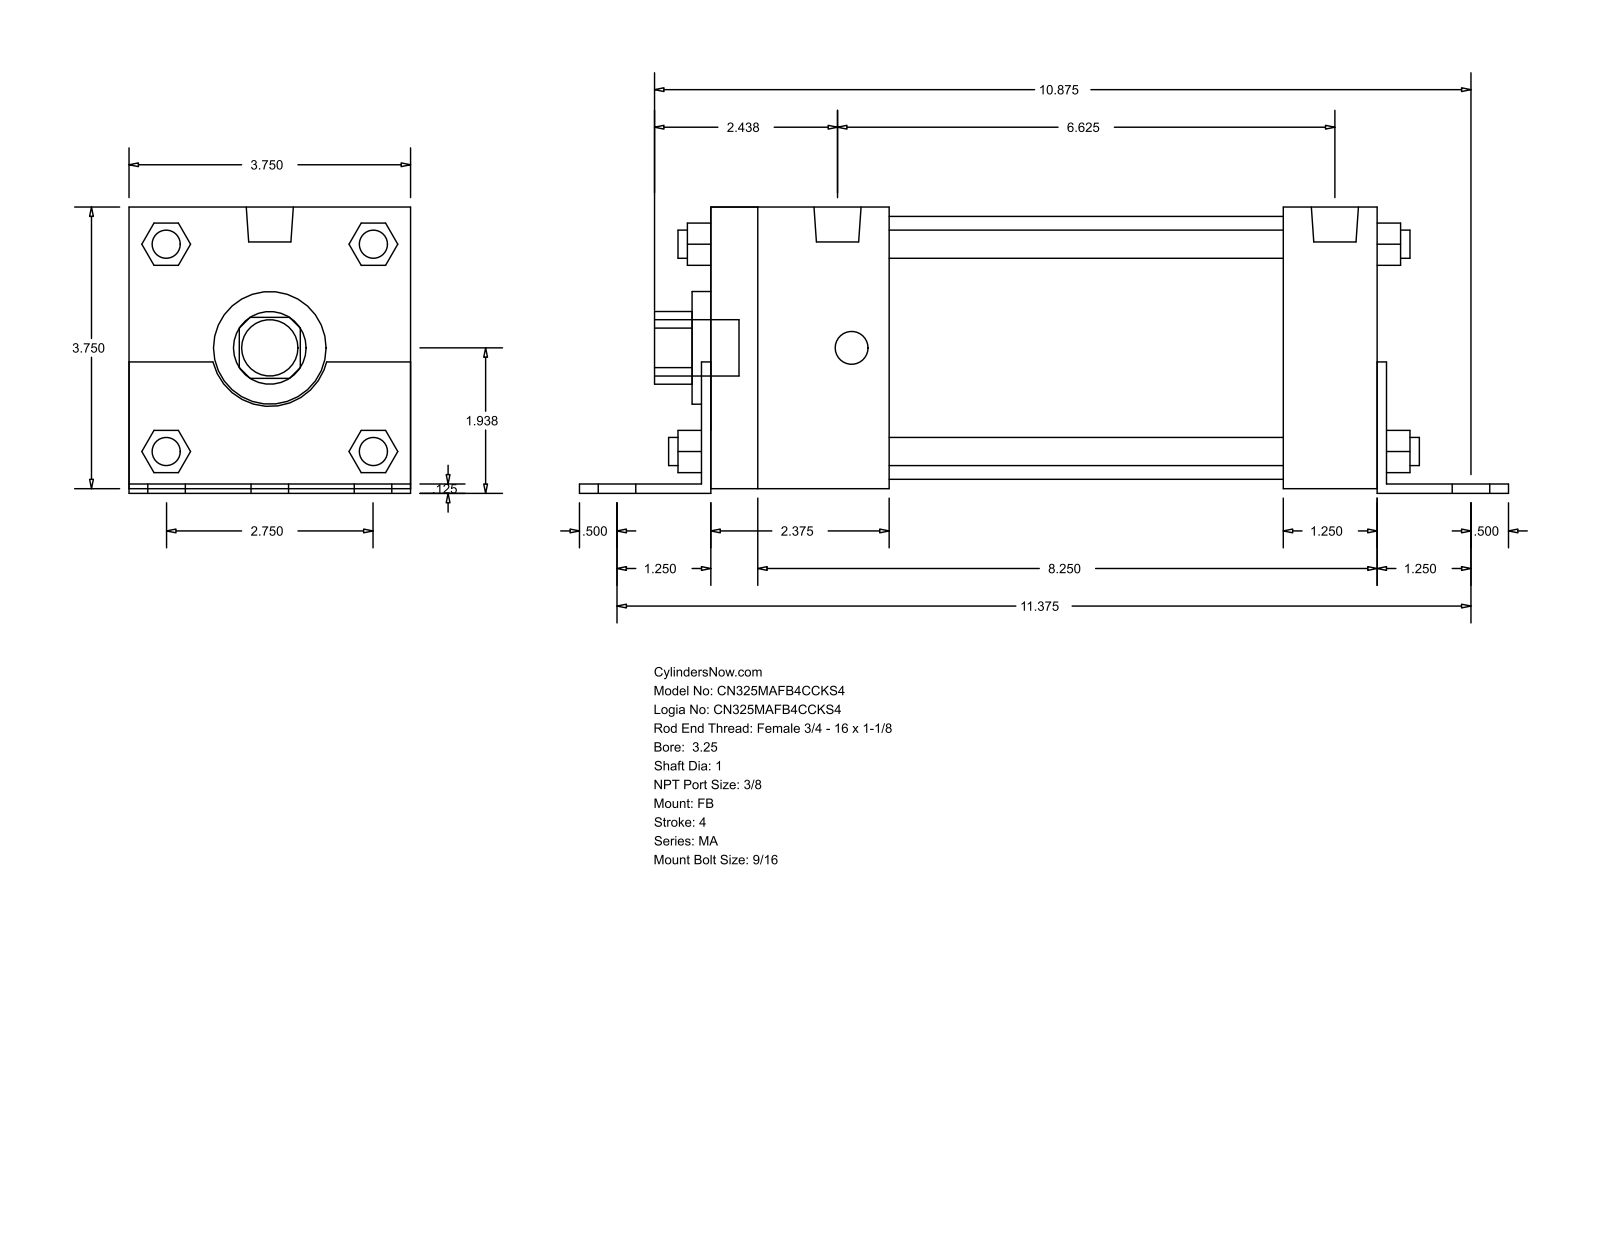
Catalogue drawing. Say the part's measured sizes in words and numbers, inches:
The part is named "MA_FB__0325_1". Its 3-D file was written by "GSSL Pune (CONFIG_CONTROL_DESIGN)". It is 0 solids with 140 faces: 105 planar, 35 cylindrical and 0 other. Overall it measures 12.375 by 3.813 by 3.75 inches. Round holes: 1 of diameter 1, 1 of diameter 1.5, 1 of diameter 3.5. Round bosses or shafts: 6 of diameter 0.563, 4 of diameter 0.437, 4 of diameter 0.375, 2 of diameter 0.627, 1 of diameter 0.75. Partial cylindrical surfaces (rounded edges, fillets, slot ends): 1 of radius 0.484, 1 of radius 0.78. The main face-to-face distances are 3.75, 0.125, 0.063, 3.812, 0.062, 3.687, 0.125, 8.875, 9.125, 9.
